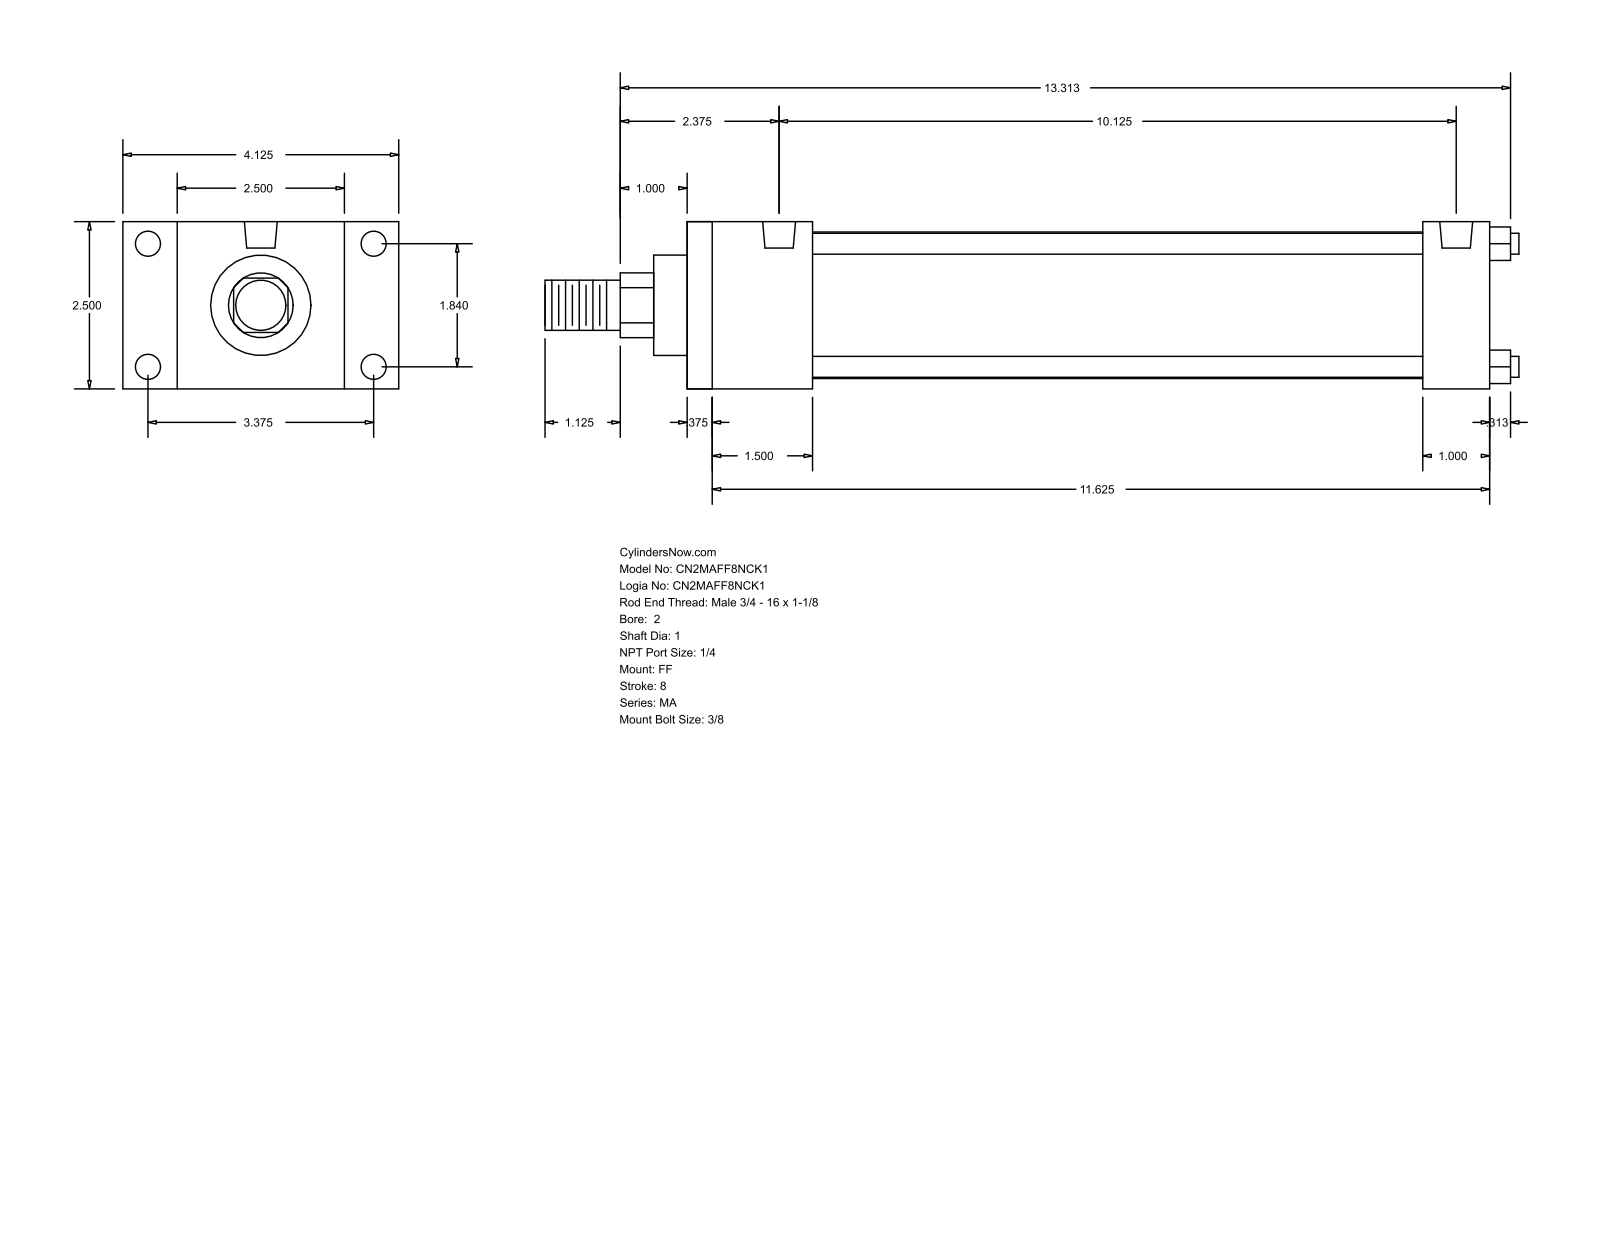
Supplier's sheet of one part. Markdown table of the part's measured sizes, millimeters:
| quantity | value |
| --- | --- |
| part name | MA_FF__0200_1 |
| STEP written by | GSSL Pune (CONFIG_CONTROL_DESIGN) |
| units | millimeters |
| bodies | 0 solids, 92 faces (64 planar, 28 cylindrical, 0 other) |
| overall size | 369.89 × 104.78 × 63.5 |
| round holes (diameter × count) | 7.94 × 4, 9.53 × 4, 12.49 × 2 |
| round bosses / shafts (diameter × count) | 7.94 × 4, 55.63 × 1, 38.1 × 1, 25.4 × 1, 19.05 × 1 |
| partial cylindrical surfaces (radius × count) | 12.29 × 1 |
| main face-to-face distances | 63.5, 304.8, 9.52, 295.28, 25.4, 20.64, 12.7, 47.63, 279.4, 38.11 |
| hole center spacings | 46.74, 85.72, 97.63, 257.17 |
